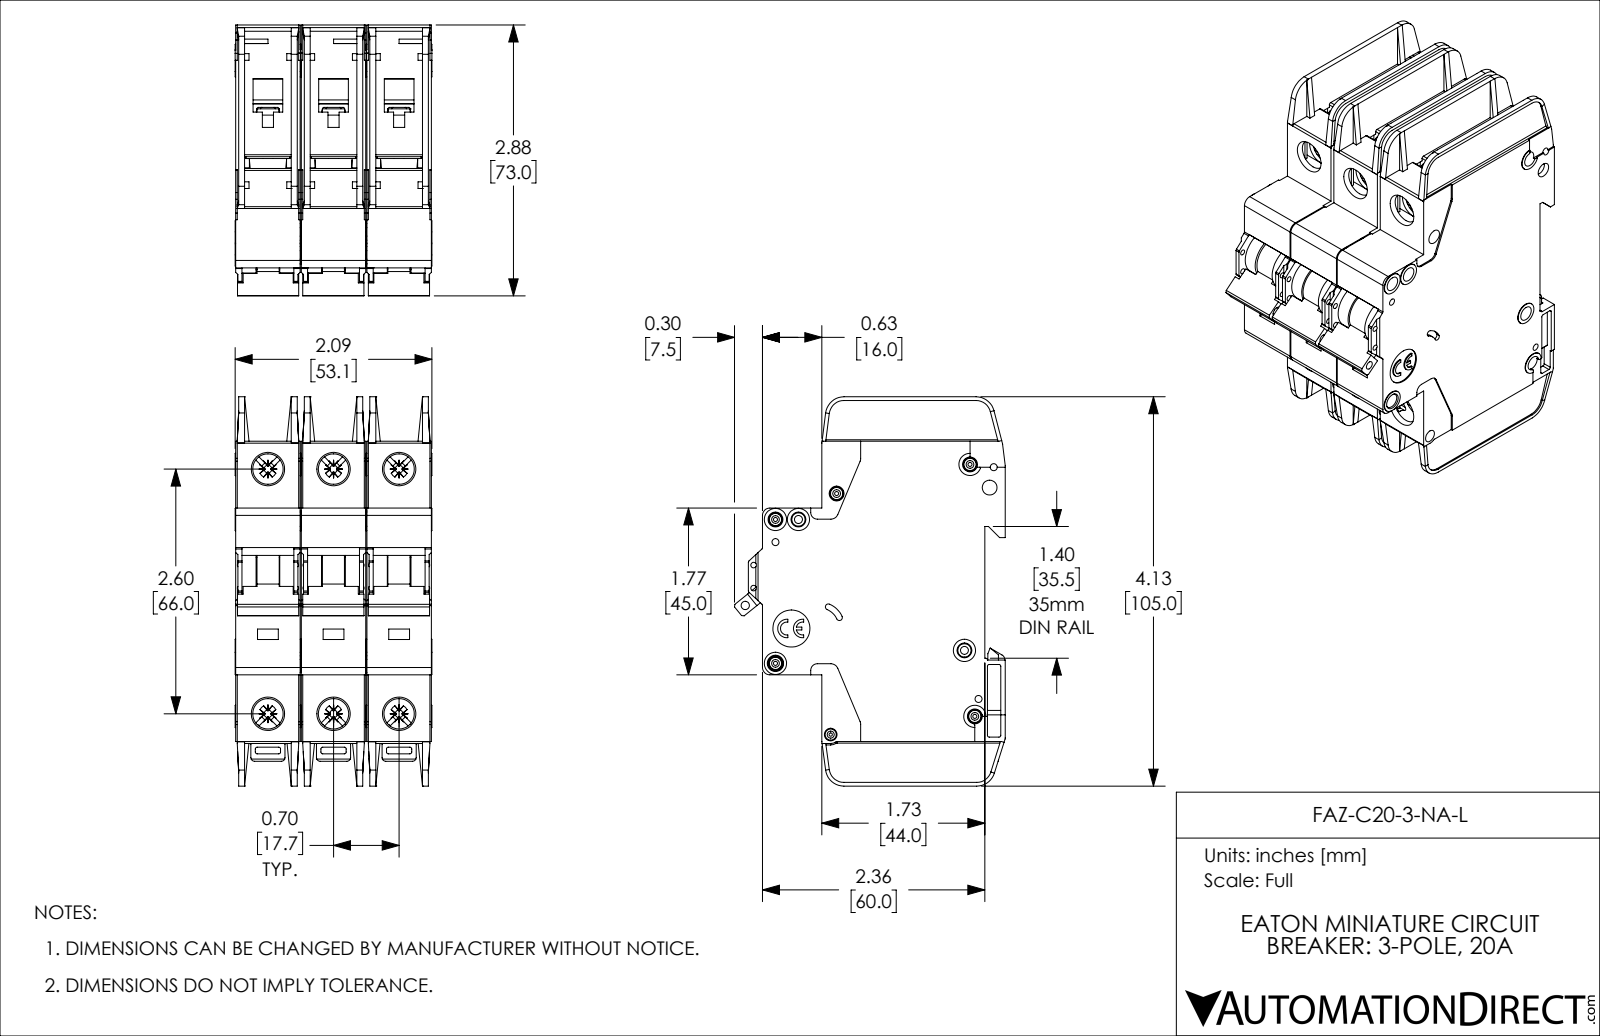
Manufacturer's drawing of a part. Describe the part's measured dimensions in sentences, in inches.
The part is named "FAZ-C20-3-NA-L". Its 3-D file was written by "SolidWorks 2019 (AUTOMOTIVE_DESIGN)". It is 3 solids with 3381 faces: 2013 planar, 1071 cylindrical and 297 other. Overall it measures 4.134 by 2.876 by 2.091 inches. Its volume is 14.05 cubic inches and its surface area 123 square inches. Round holes: 8 of diameter 0.157, 6 of diameter 0.323, 5 of diameter 0.043, 4 of diameter 0.075, 2 of diameter 0.059, 2 of diameter 0.085, 1 of diameter 0.035, 1 of diameter 0.089, 1 of diameter 0.098, 1 of diameter 0.134, 1 of diameter 0.394. Round bosses or shafts: 5 of diameter 0.13, 4 of diameter 0.236, 4 of diameter 0.118, 3 of diameter 0.098. Partial cylindrical surfaces (rounded edges, fillets, slot ends): 72 of radius 0.02, 30 of radius 0.016, 18 of radius 0.039, 12 of radius 0.043, 12 of radius 0.079, 6 of radius 0.008, 6 of radius 0.01, 6 of radius 0.028. The main face-to-face distances are 0.697, 0.047, 1.394, 0.685, 0.591, 1.382, 0.744, 0.65, 0.106, 0.094. The hole center spacings are 0.697, 2.69, 2.598, 0.244, 0.537, 0.87, 1.394, 2.948.
